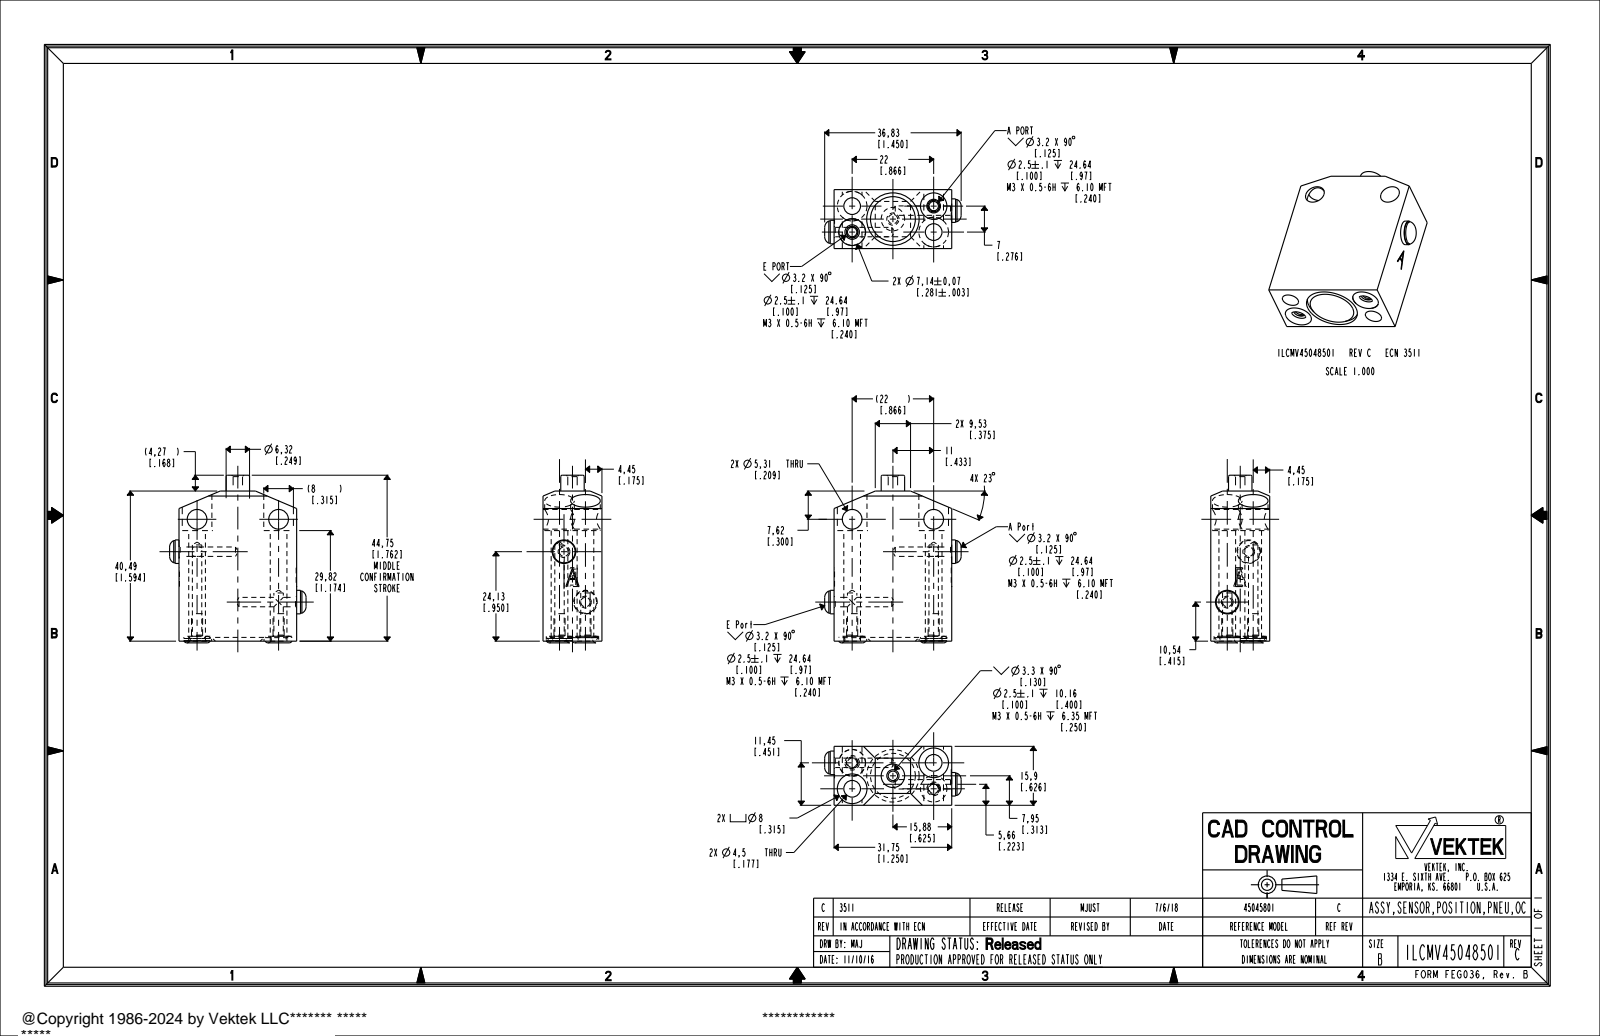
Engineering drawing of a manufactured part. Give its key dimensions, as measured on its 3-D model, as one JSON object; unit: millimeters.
{"part_name": "ILCMV45048501", "step_written_by": "PRO/ENGINEER BY PARAMETRIC TECHNOLOGY CORPORATION, 2013320 (AUTOMOTIVE_DESIGN)", "units": "millimeters", "bodies": {"solids": 1, "faces": 134, "planar": 50, "cylindrical": 54, "other": 30}, "overall_size": [45.2, 36.8, 15.9], "volume_mm3": 17300, "surface_area_mm2": 6974, "round_holes": [[2.5, 5], [4.5, 2], [5.3, 2], [7.1, 2], [8, 2], [14.1, 1]], "round_bosses_or_shafts": [[6.4, 2], [3, 2], [6.3, 1], [6, 1], [6, 1]], "face_to_face_distances": [15.9, 31.8, 29.8, 10.7, 40.5, 39.2, 28.5, 1.3, 4.3, 14.9], "hole_center_spacings": [11.5, 22, 7, 23.1, 14.8]}
